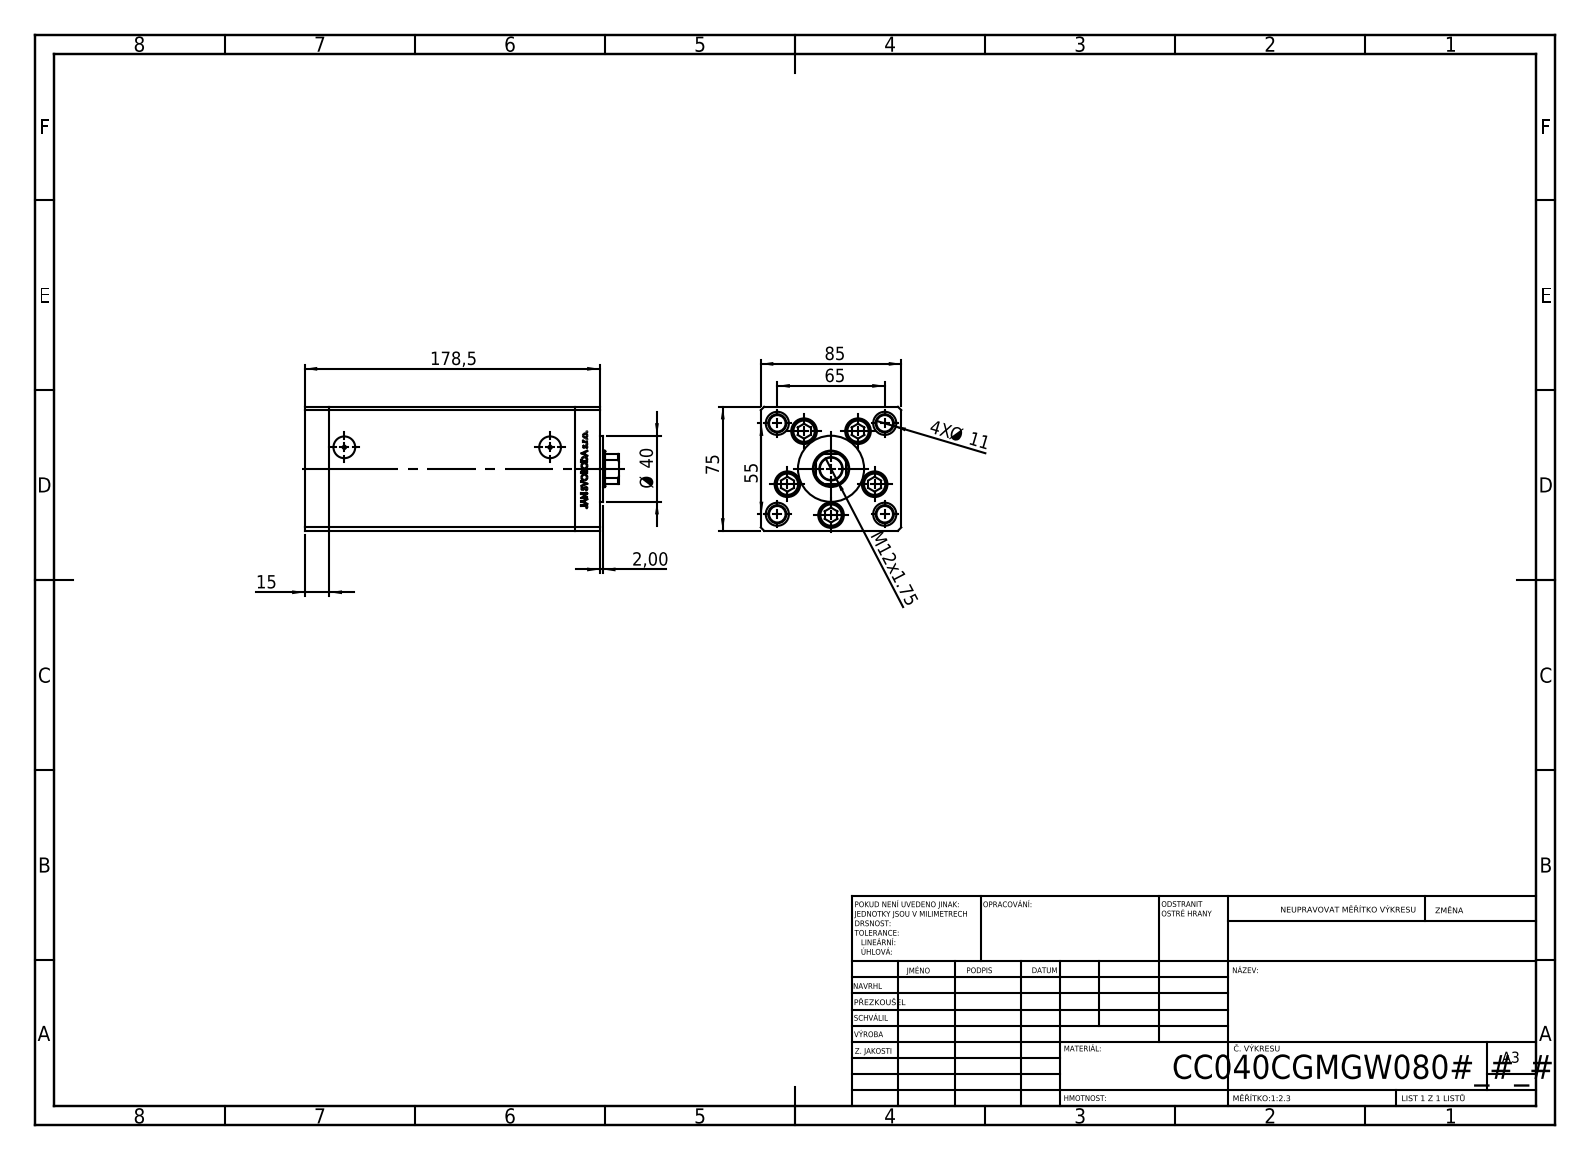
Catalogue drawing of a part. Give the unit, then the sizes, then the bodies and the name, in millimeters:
Units: millimetres
Overall size (bounding box): 190 × 85 × 75
Round holes (diameter × count): ⌀11 ×9, ⌀15.5 ×5, ⌀10 ×4, ⌀14 ×4, ⌀2 ×2, ⌀13.16 ×2, ⌀13.5 ×1, ⌀14.5 ×1, ⌀22 ×1
Round bosses / shafts (diameter × count): ⌀8 ×5, ⌀14.5 ×4, ⌀40 ×1
Partial cylindrical surfaces — rounded edges, fillets, slot ends (radius × count): R0.93 ×2, R10.5 ×1
Main face-to-face distances: 85, 75, 15, 148.5, 163.5, 10.5, 178.5, 34.25, 144.25, 129.25
Hole centre spacings: 28, 42.57, 16.86, 19.17, 32.33, 32.5, 33.63, 37.33
Volume: 945 382 mm³ · Surface area: 180 492 mm²
Bodies: 13 solids, 1171 faces (542 planar, 167 cylindrical, 462 other)
Part name (STEP PRODUCT): ALLEN BOLT; V220C_C MIDDLE; V220C FRONT; V220C_VC_C (+1 more)
STEP written by: SolidWorks 2019 (CONFIG_CONTROL_DESIGN)
